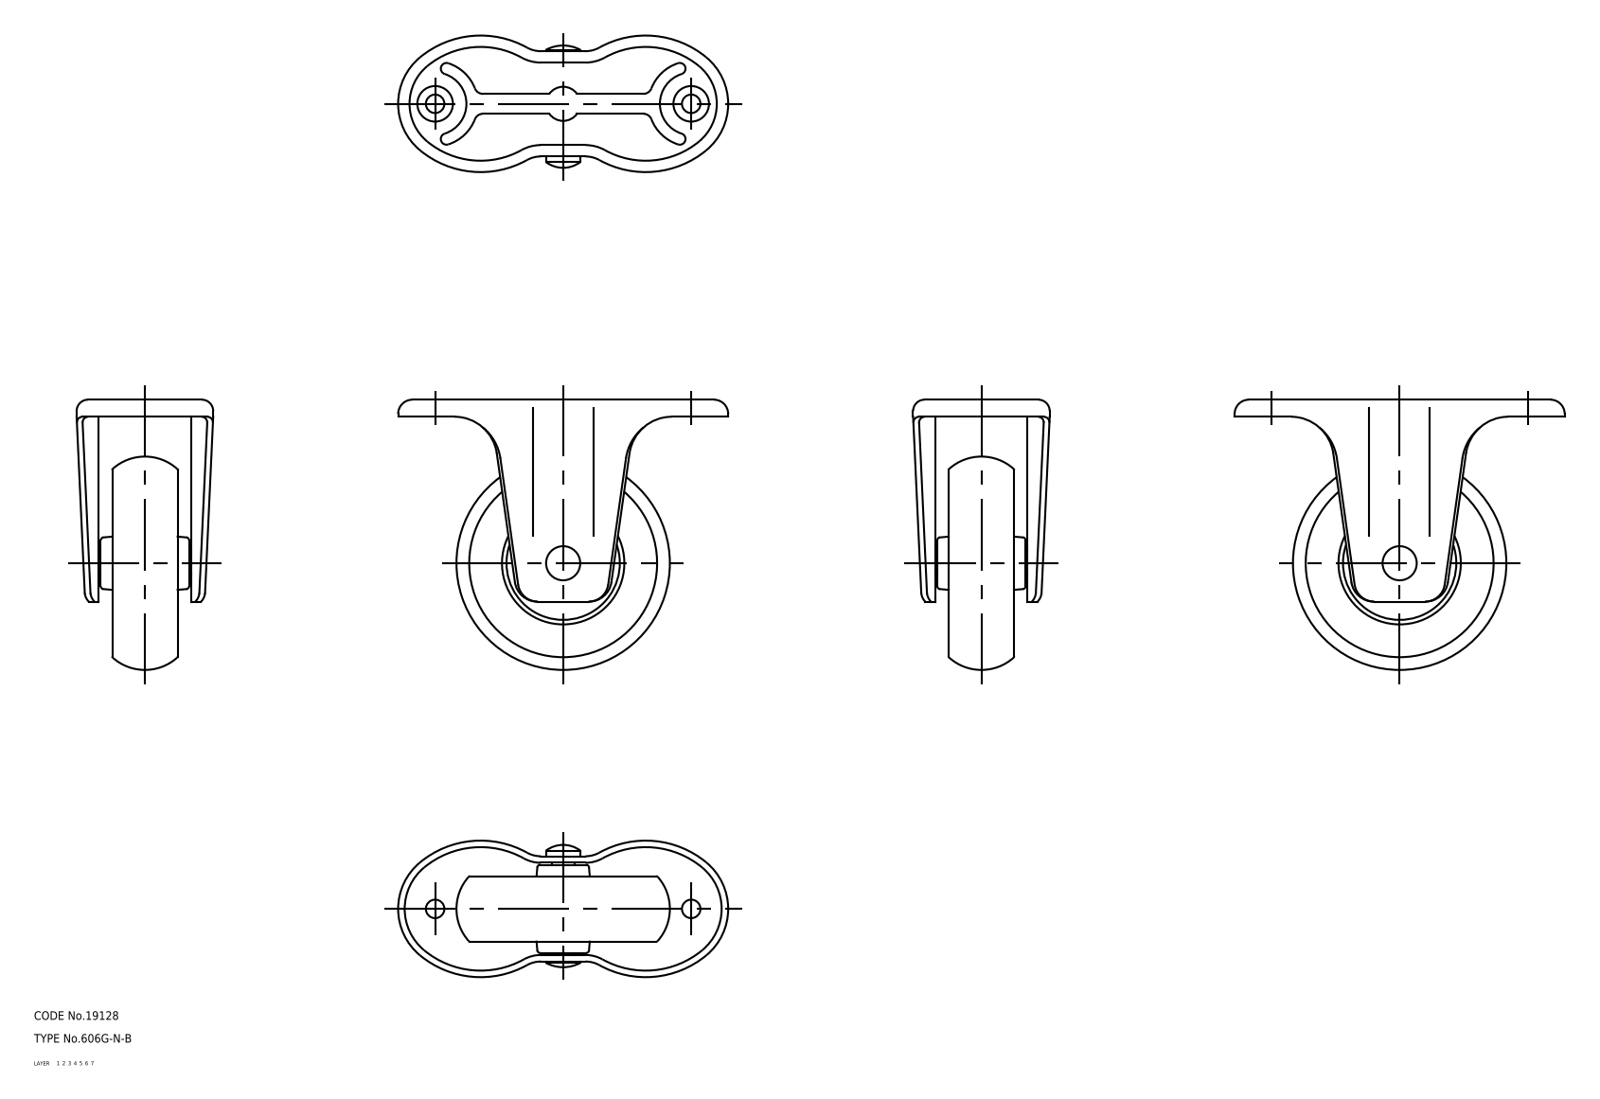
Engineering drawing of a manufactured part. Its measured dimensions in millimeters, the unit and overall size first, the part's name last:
Units: millimetres
Overall size (bounding box): 116 × 95 × 48
Volume: 105 669 mm³ · Surface area: 40 879 mm²
Bodies: 3 solids, 185 faces (0 planar, 0 cylindrical, 185 other)
Part name (STEP PRODUCT): wheel; axle; No_606G_N_B_16360_36
STEP written by: CADfix (AUTOMOTIVE_DESIGN)
